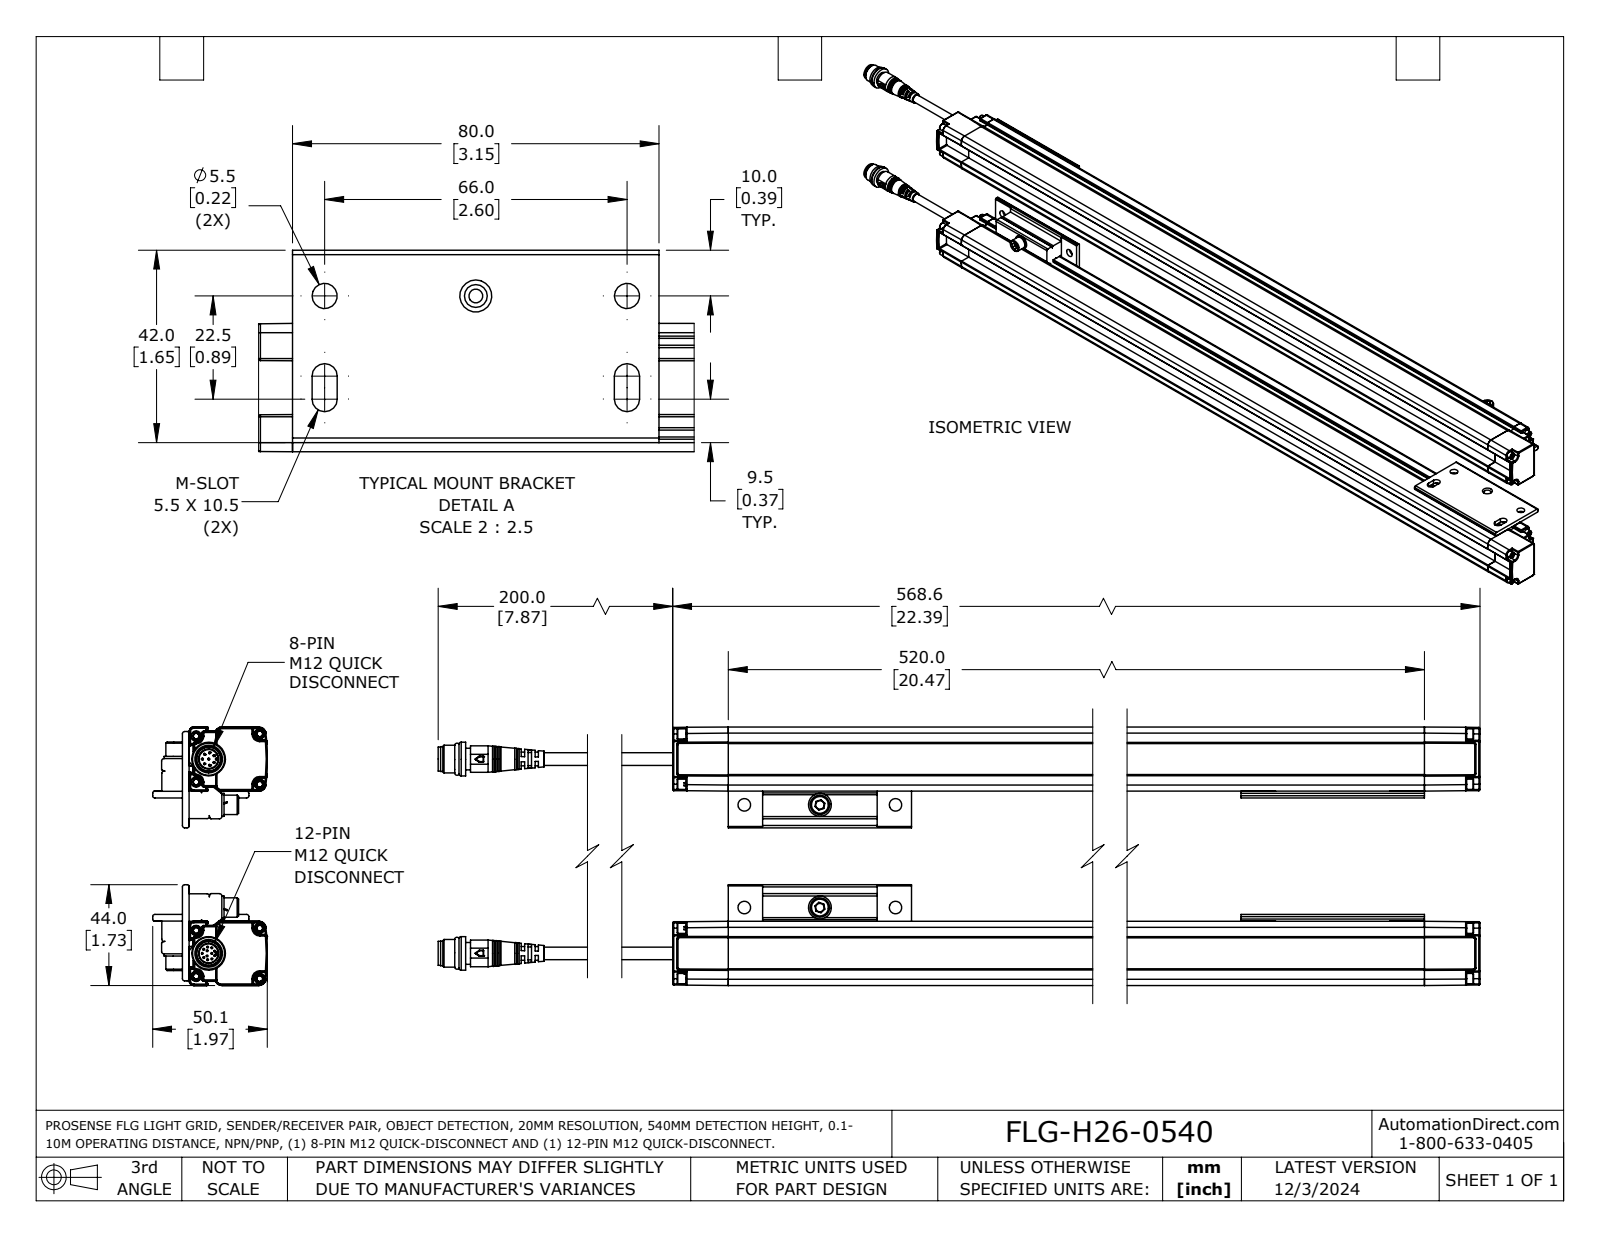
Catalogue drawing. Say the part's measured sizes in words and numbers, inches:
The part is named "FLG-H26-0540". Its 3-D file was written by "SolidWorks 2023 (AUTOMOTIVE_DESIGN)". It is 10 solids with 1668 faces: 816 planar, 456 cylindrical and 396 other. Overall it measures 26.006 by 4.441 by 1.972 inches. Its volume is 58.25 cubic inches and its surface area 398.8 square inches. Round holes: 16 of diameter 0.016, 6 of diameter 0.217, 4 of diameter 0.098, 3 of diameter 0.197, 2 of diameter 0.327. Round bosses or shafts: 20 of diameter 0.031, 8 of diameter 0.177, 8 of diameter 0.118, 4 of diameter 0.217, 4 of diameter 0.059, 3 of diameter 0.394, 3 of diameter 0.335, 3 of diameter 0.146. Partial cylindrical surfaces (rounded edges, fillets, slot ends): 142 of radius 0.02, 40 of radius 0.039, 20 of radius 0.01, 12 of radius 0.008, 12 of radius 0.012, 12 of radius 0.108, 6 of radius 0.1, 4 of radius 0.049. The main face-to-face distances are 3.339, 1.102, 0.071, 0.285, 0.817, 2.236, 0.97, 0.118, 4.441, 1.041. The hole center spacings are 0.108, 1.299, 0.163, 0.979, 2.191, 0.215, 1.764, 2.598.
